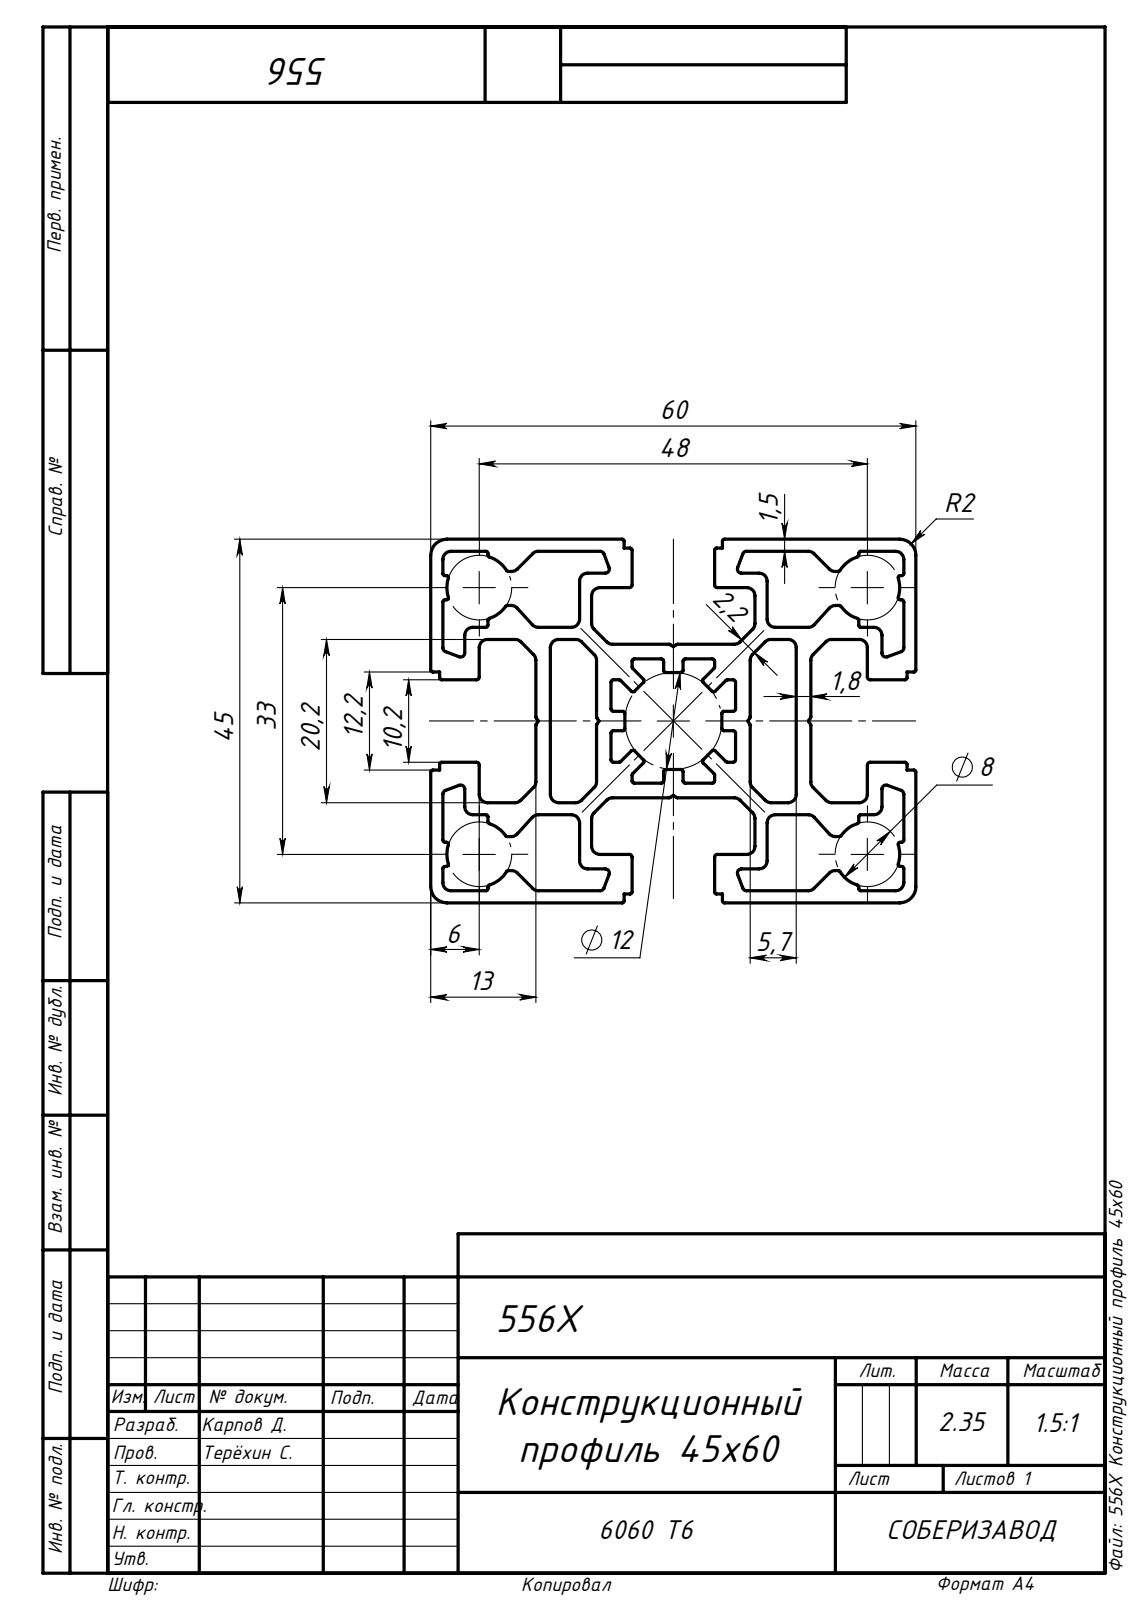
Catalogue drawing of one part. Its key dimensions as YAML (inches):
part_name: "556X Конструкционный профиль 45х60"
step_written_by: "SolidWorks 2019 (AUTOMOTIVE_DESIGN)"
units: inches
bodies: {solids: 1, faces: 436, planar: 208, cylindrical: 228, other: 0}
overall_size: [39.37, 2.362, 1.772]
volume: 53.18
surface_area: 1296
partial_cylinders:
  - {radius: 0.01, count: 84}
  - {radius: 0.039, count: 68}
  - {radius: 0.012, count: 24}
  - {radius: 0.02, count: 16}
  - {radius: 0.014, count: 8}
  - {radius: 0.079, count: 4}
  - {radius: 0.157, count: 4}
face_to_face_distances: [0.059, 0.071, 0.748, 0.512, 0.453, 0.295, 0.583, 0.083, 1.713, 1.283]
